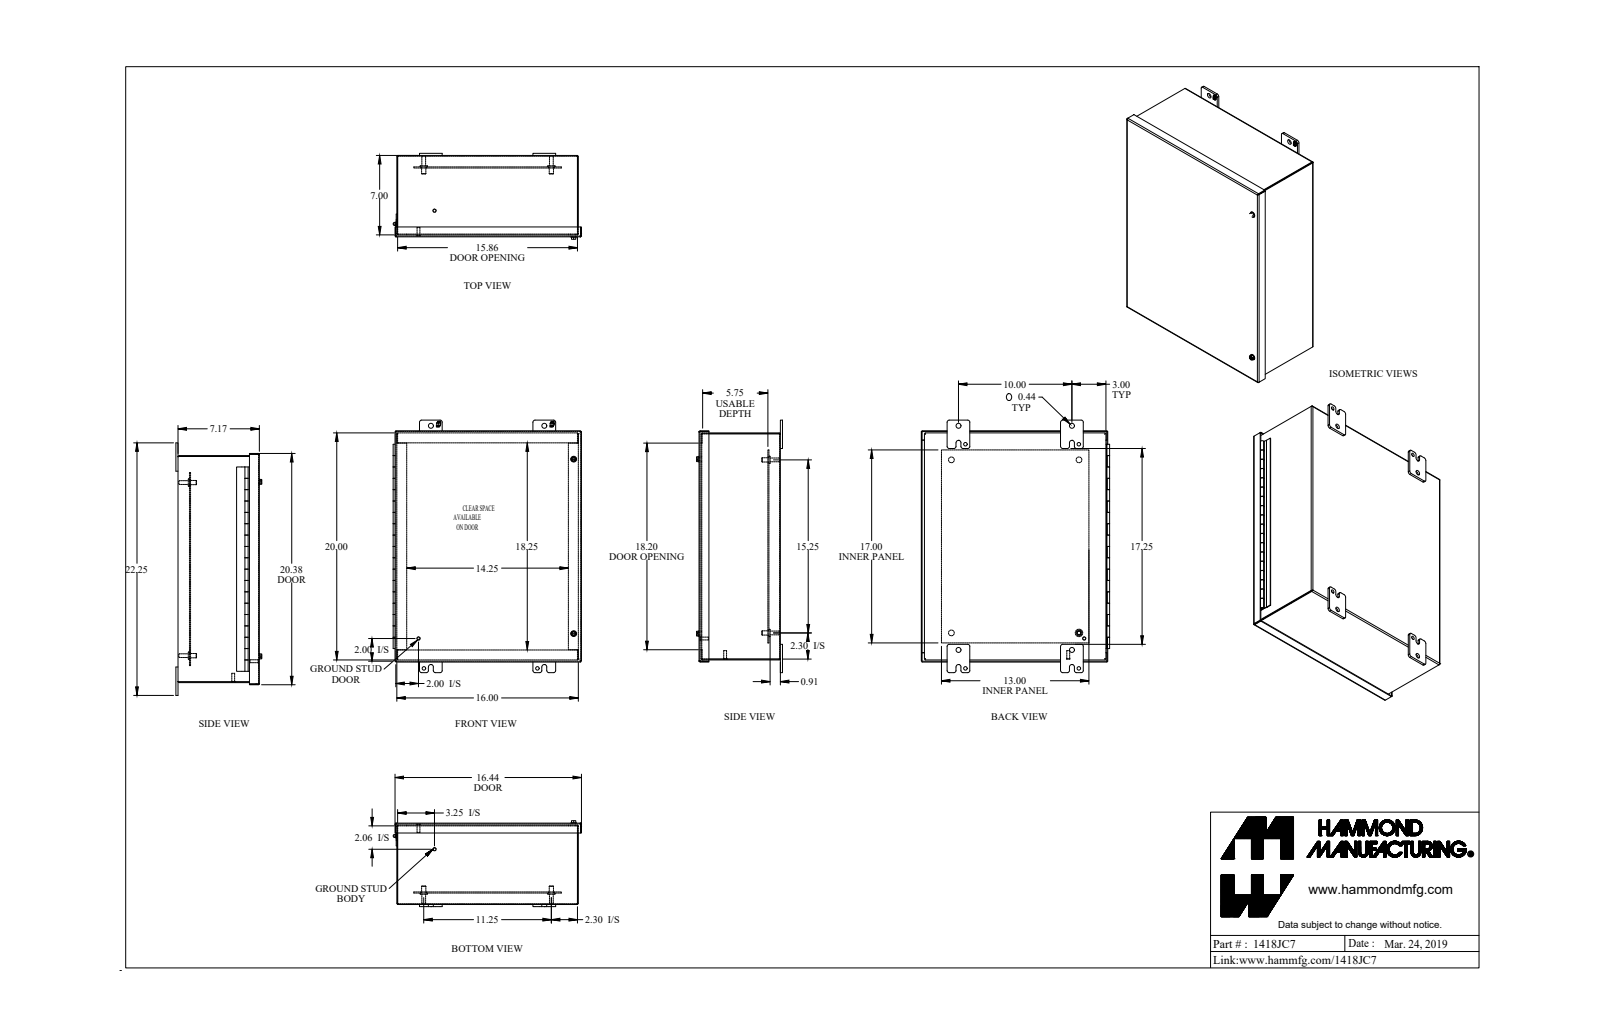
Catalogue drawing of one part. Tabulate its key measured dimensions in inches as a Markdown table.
| quantity | value |
| --- | --- |
| part name | 1418JC7 |
| STEP written by | SolidWorks 2019 (AUTOMOTIVE_DESIGN) |
| units | inches |
| bodies | 25 solids, 612 faces (408 planar, 160 cylindrical, 44 other) |
| overall size | 22.25 × 16.604 × 7.571 |
| volume | 133.8 in³ |
| surface area | 3 295 in² |
| round holes (diameter × count) | 0.313 × 6, 0.437 × 4, 0.5 × 4, 0.266 × 2, 0.307 × 2, 0.397 × 2, 0.445 × 2, 0.187 × 1 |
| round bosses / shafts (diameter × count) | 0.65 × 4, 0.375 × 4, 0.33 × 4, 1 × 2, 0.541 × 2, 0.281 × 2, 0.25 × 2, 0.244 × 2 |
| partial cylindrical surfaces (radius × count) | 0.188 × 24, 0.007 × 20, 0.079 × 20, 0.218 × 8, 0.029 × 2, 0.079 × 2 |
| main face-to-face distances | 0.072, 7.1, 7.172, 7.028, 15.928, 6.091, 1.104, 1.032, 5.996, 6.068 |
| hole center spacings | 18.951, 1.736, 10, 11.25, 19.75, 22.137, 1.966, 3.065 |
